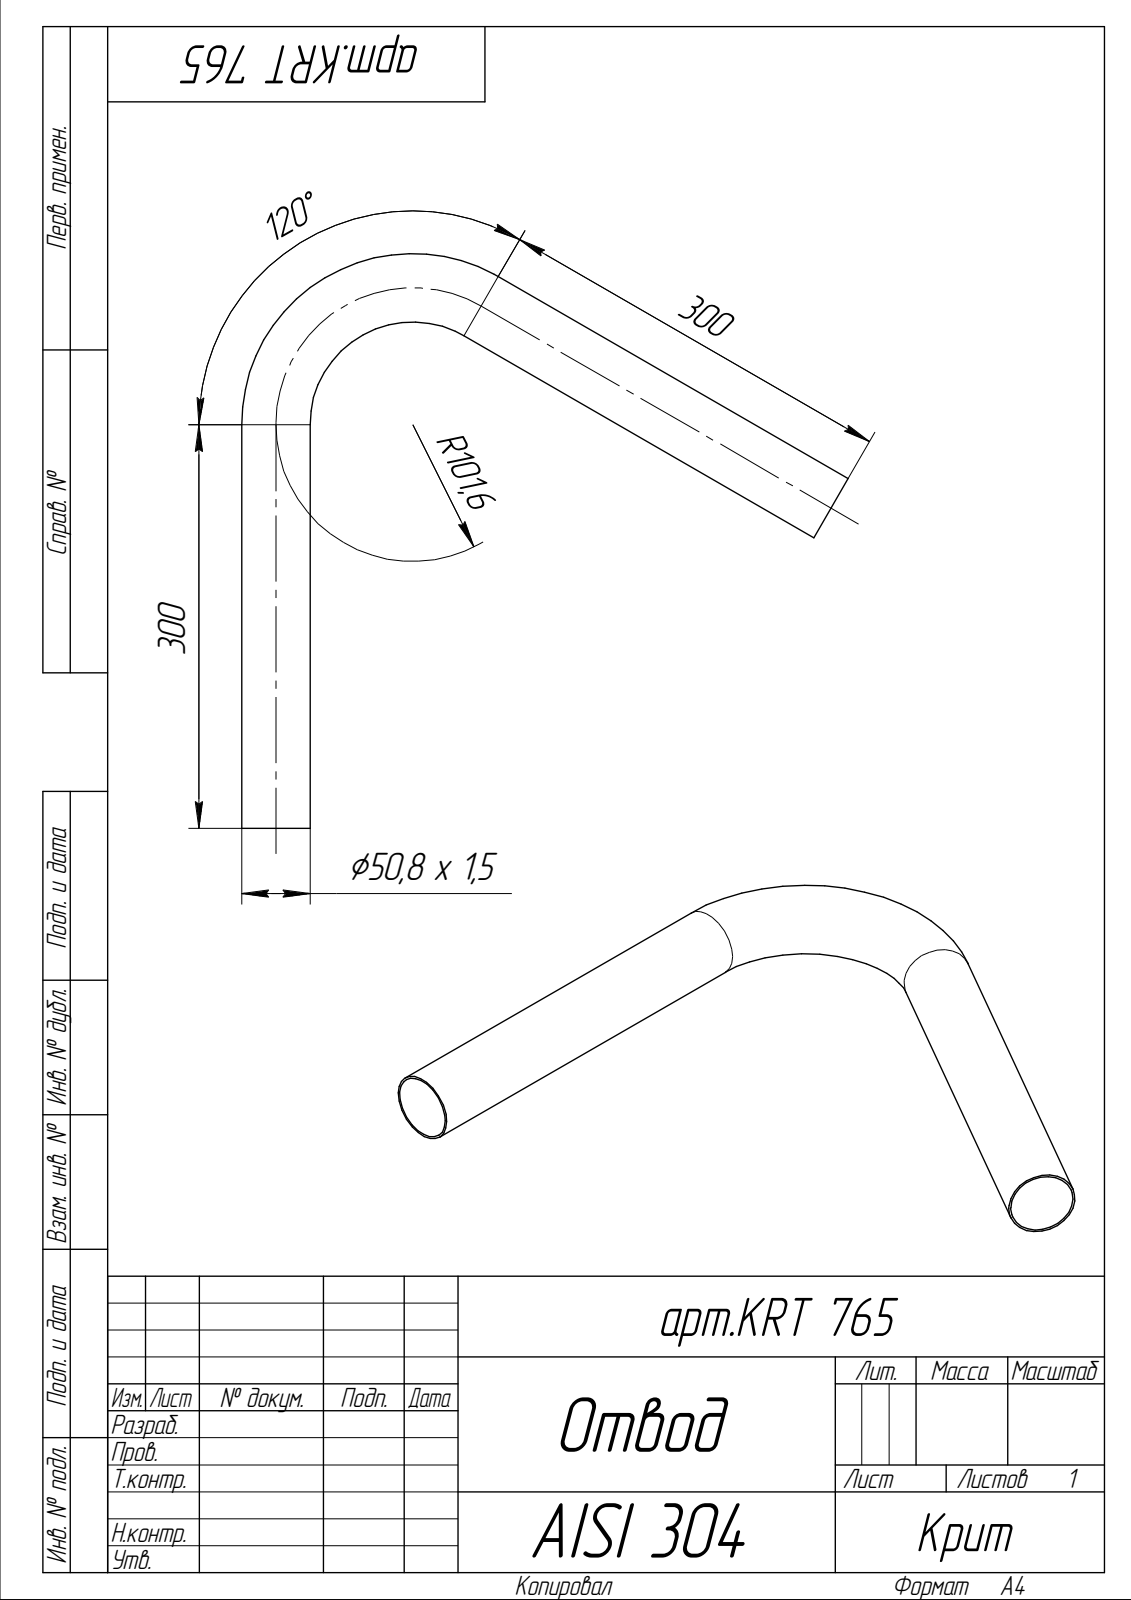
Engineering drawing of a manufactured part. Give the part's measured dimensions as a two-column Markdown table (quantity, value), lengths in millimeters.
| quantity | value |
| --- | --- |
| part name | Деталь |
| STEP written by | ASCON Math Kernel (AUTOMOTIVE_DESIGN) |
| units | millimeters |
| bodies | 1 solid, 8 faces (2 planar, 4 cylindrical, 2 other) |
| overall size | 450.31 × 427 × 50.8 |
| volume | 188 828 mm³ |
| surface area | 252 235 mm² |
| round holes (diameter × count) | 47.8 × 2 |
| round bosses / shafts (diameter × count) | 50.8 × 2 |
